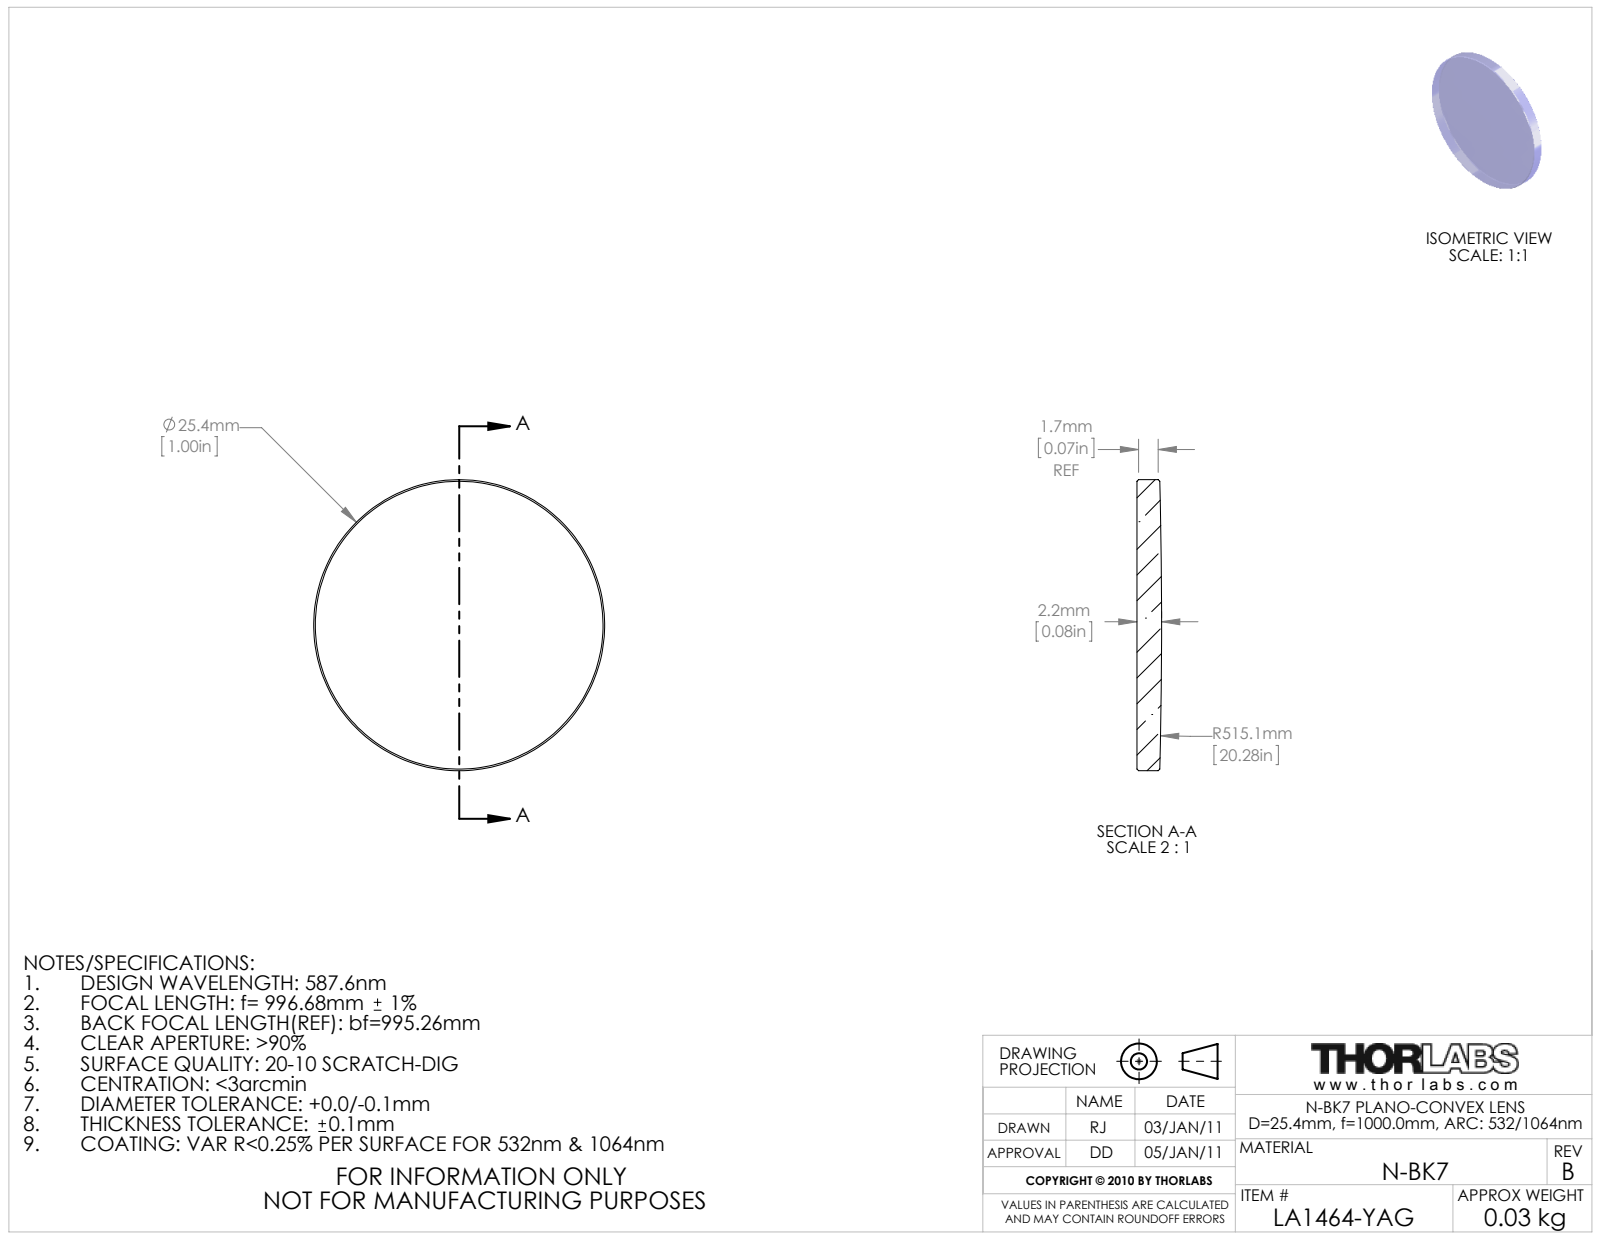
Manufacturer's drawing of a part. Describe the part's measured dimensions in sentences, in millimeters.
The part is named "21806-E0W". Its 3-D file was written by "SolidWorks 2011 (AUTOMOTIVE_DESIGN)". It is 0 solids with 9 faces: 1 planar, 2 cylindrical and 6 other. Overall it measures 25.4 by 25.4 by 2.15 millimeters. Round bosses or shafts: 1 of diameter 25.4.
